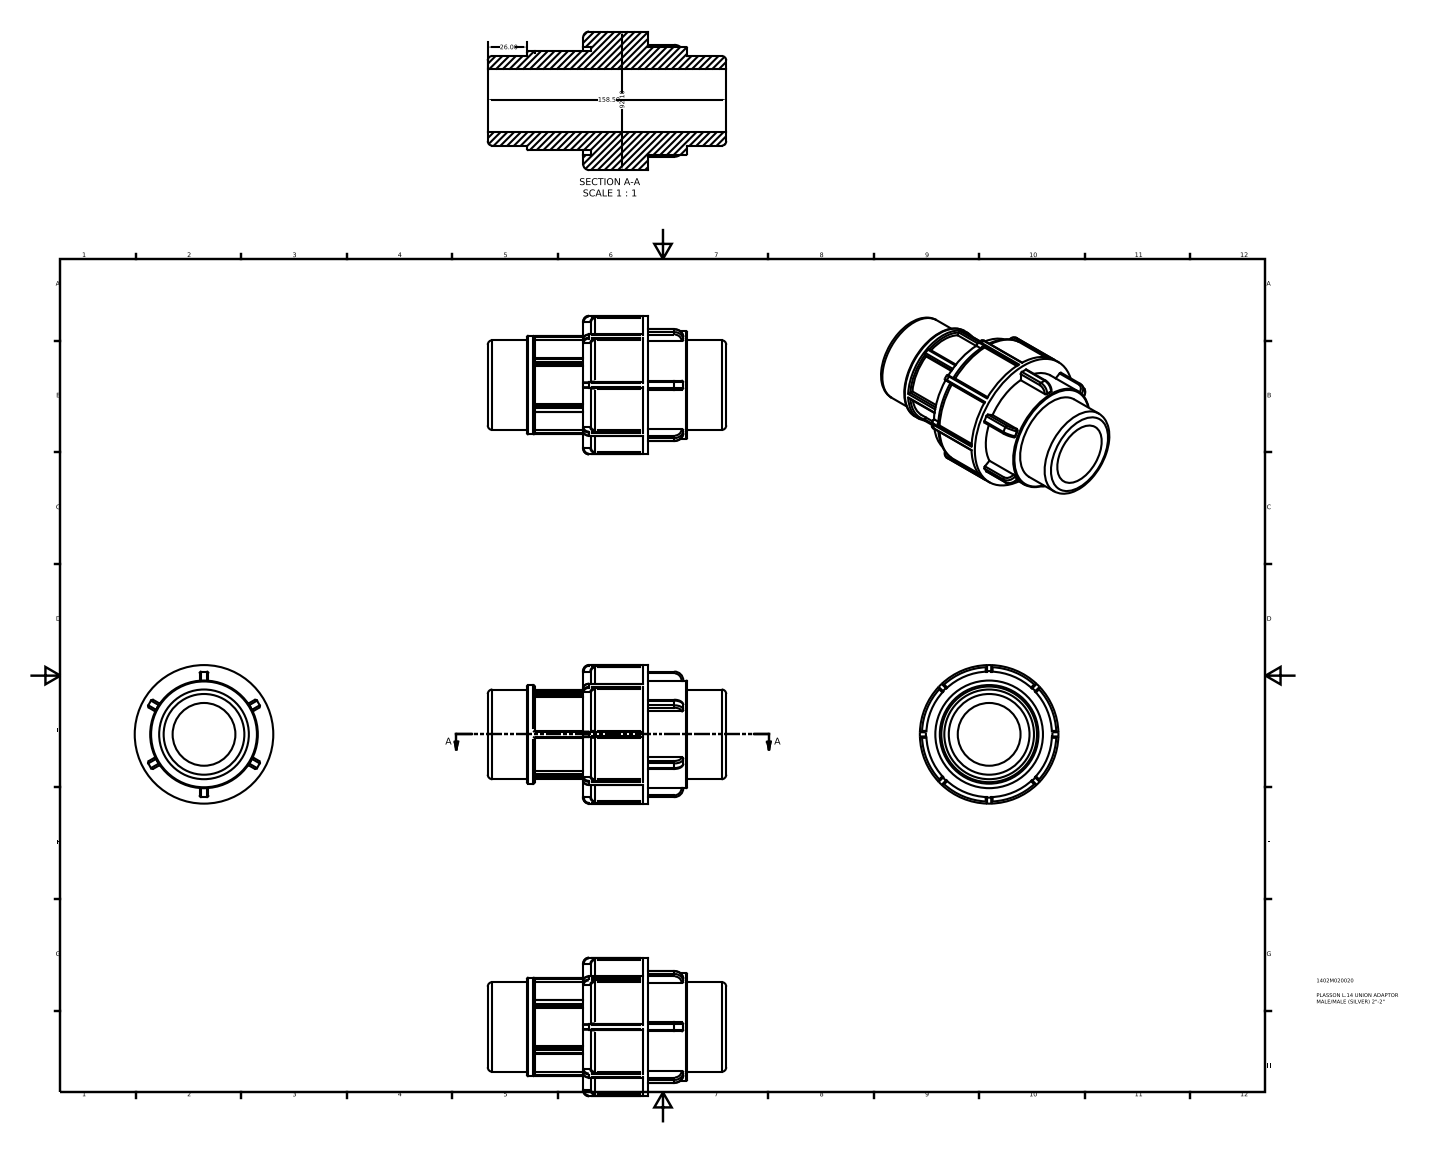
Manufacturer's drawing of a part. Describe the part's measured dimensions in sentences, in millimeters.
The part is named "1402M020020". Its 3-D file was written by "Autodesk Inventor 2015 (AUTOMOTIVE_DESIGN)". It is 1 solid with 273 faces: 84 planar, 124 cylindrical and 65 other. Overall it measures 158.5 by 92.1 by 92.1 millimeters. Its volume is 409 024 cubic millimeters and its surface area 71 592 square millimeters. Round holes: 1 of diameter 41.73, 1 of diameter 71.54. Round bosses or shafts: 1 of diameter 92.1, 1 of diameter 89.34, 1 of diameter 83.46, 1 of diameter 65.58, 1 of diameter 59.61. Partial cylindrical surfaces (rounded edges, fillets, slot ends): 44 of radius 0.46, 22 of radius 1.19, 12 of radius 1, 6 of radius 5.96. The main face-to-face distances are 5.2, 42.8, 132.5, 26, 37.6, 69.1, 63.9, 26.3, 63.4, 68.6.
